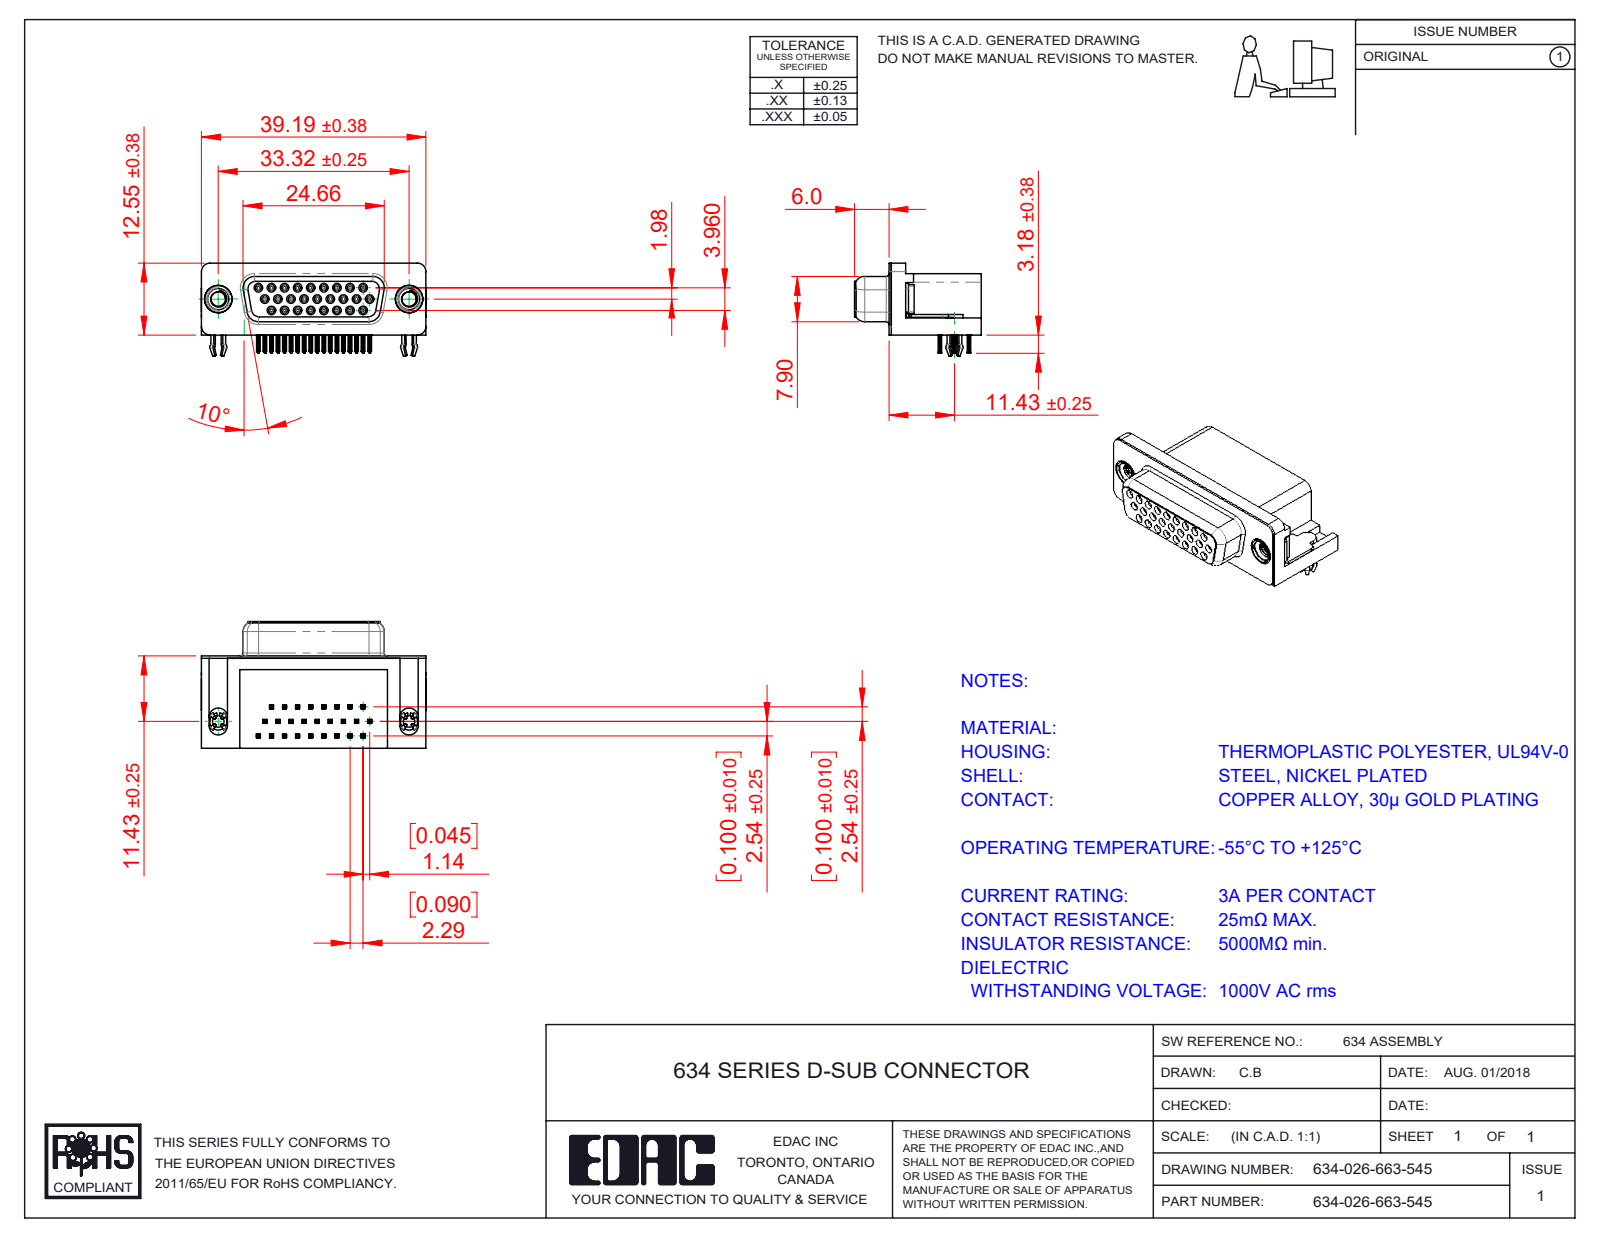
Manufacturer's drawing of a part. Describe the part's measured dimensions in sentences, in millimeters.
The part is named "4 Prong Board Lock; M3 Threaded Rivet; Contact Middle; Contact Bottom (+4 more)". Its 3-D file was written by "SolidWorks 2016 (CONFIG_CONTROL_DESIGN)". It is 32 solids with 4101 faces: 1813 planar, 948 cylindrical and 1340 other. Overall it measures 39.22 by 22.1 by 16.25 millimeters. Its volume is 6 370 cubic millimeters and its surface area 9 157 square millimeters. Round holes: 26 of diameter 0.8, 26 of diameter 0.9, 2 of diameter 2, 2 of diameter 2.5, 2 of diameter 4, 2 of diameter 4.8, 2 of diameter 5. Round bosses or shafts: 26 of diameter 1.2, 2 of diameter 4.9, 2 of diameter 4.75, 2 of diameter 3.9, 2 of diameter 3. Partial cylindrical surfaces (rounded edges, fillets, slot ends): 208 of radius 0.1, 104 of radius 0.15, 52 of radius 0.35, 26 of radius 0.34, 19 of radius 1, 12 of radius 0.25, 8 of radius 0.28, 8 of radius 1.35. The main face-to-face distances are 0.4, 10.34, 15.7, 0.35, 16.1, 6.65, 2.5, 0.85, 2.9, 10.69. The hole center spacings are 2.29, 4.57, 2.28, 3.96, 6.05, 2.3, 2.27, 4.58.
